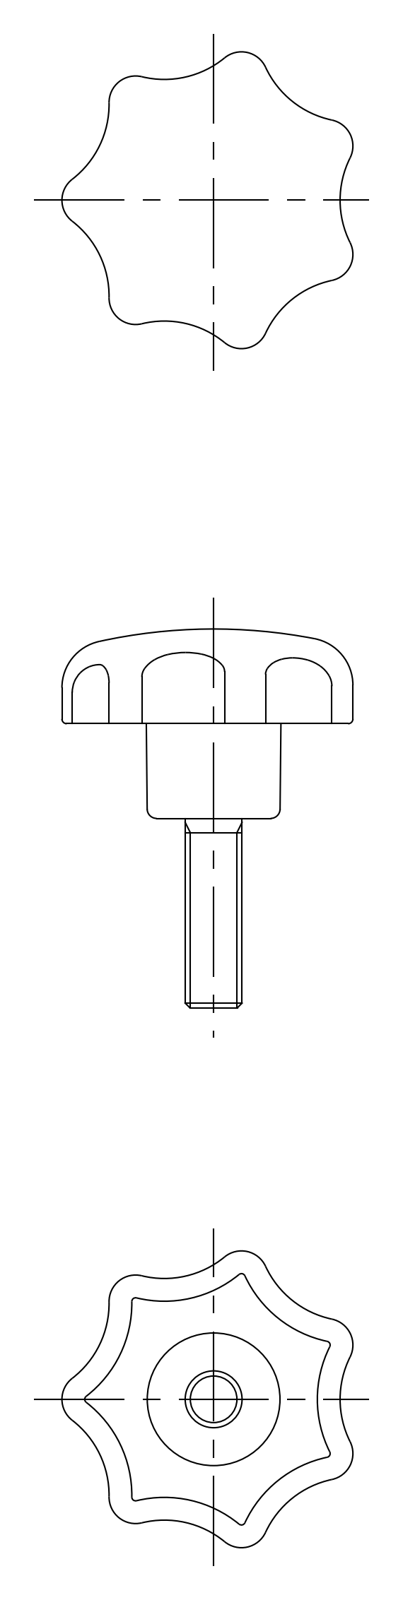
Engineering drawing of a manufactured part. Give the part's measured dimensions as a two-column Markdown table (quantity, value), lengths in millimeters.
| quantity | value |
| --- | --- |
| part name | screw; knob; KSM_32_M6_20_24516_36 |
| STEP written by | CADfix (AUTOMOTIVE_DESIGN) |
| units | millimeters |
| bodies | 2 solids, 106 faces (0 planar, 0 cylindrical, 106 other) |
| overall size | 40 × 31.34 × 30.69 |
| volume | 5 965 mm³ |
| surface area | 4 298 mm² |
